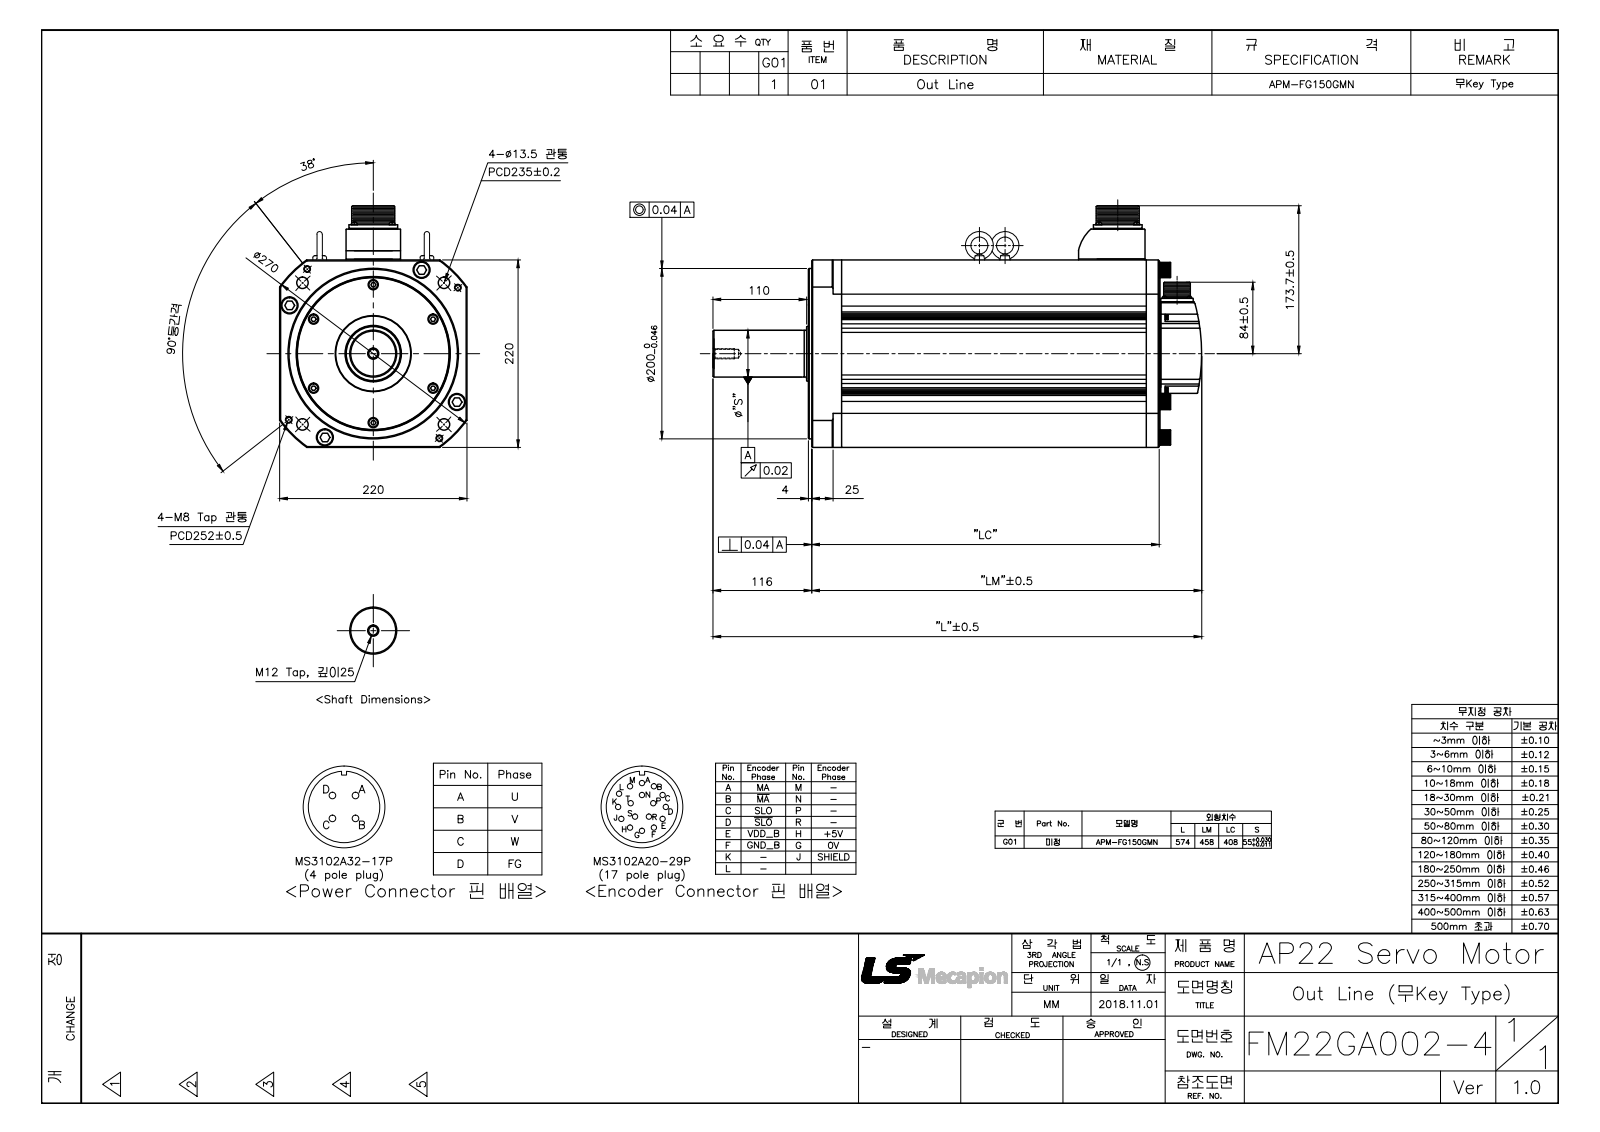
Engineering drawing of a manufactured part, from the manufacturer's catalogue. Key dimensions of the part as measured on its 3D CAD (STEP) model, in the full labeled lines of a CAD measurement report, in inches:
Part name (STEP PRODUCT): FM22GA002-4_Out Line(APM-FG150G_N)
STEP written by: SolidWorks 2011 (AUTOMOTIVE_DESIGN)
Units: inches
Bodies: 64 solids, 2136 faces (738 planar, 852 cylindrical, 546 other)
Overall size (bounding box): 22.598 × 11.169 × 8.661
Volume: 1 087 in³ · Surface area: 1 553 in²
Round holes (diameter × count): ⌀0.472 ×10, ⌀0.098 ×8, ⌀0.118 ×8, ⌀0.268 ×8, ⌀0.531 ×8, ⌀0.787 ×8, ⌀0.12 ×6, ⌀0.197 ×6, ⌀0.236 ×6, ⌀0.276 ×6, ⌀0.315 ×6, ⌀0.402 ×5
Round bosses / shafts (diameter × count): ⌀0.063 ×17, ⌀0.402 ×6, ⌀0.394 ×6, ⌀0.709 ×4, ⌀0.276 ×4, ⌀0.236 ×4, ⌀0.217 ×4, ⌀0.213 ×4
Partial cylindrical surfaces — rounded edges, fillets, slot ends (radius × count): R0.039 ×117, R0.079 ×17, R0.197 ×16, R0.177 ×12, R0.02 ×8, R0.157 ×4, R0.236 ×4, R0.012 ×2
Main face-to-face distances: 14.094, 1.575, 8.661, 7.087, 0.669, 0.63, 0.551, 5.512, 15.63, 0.197
Hole centre spacings: 3.189, 5.524, 0.674, 0.819, 1.157, 1.197, 1.239, 1.731
